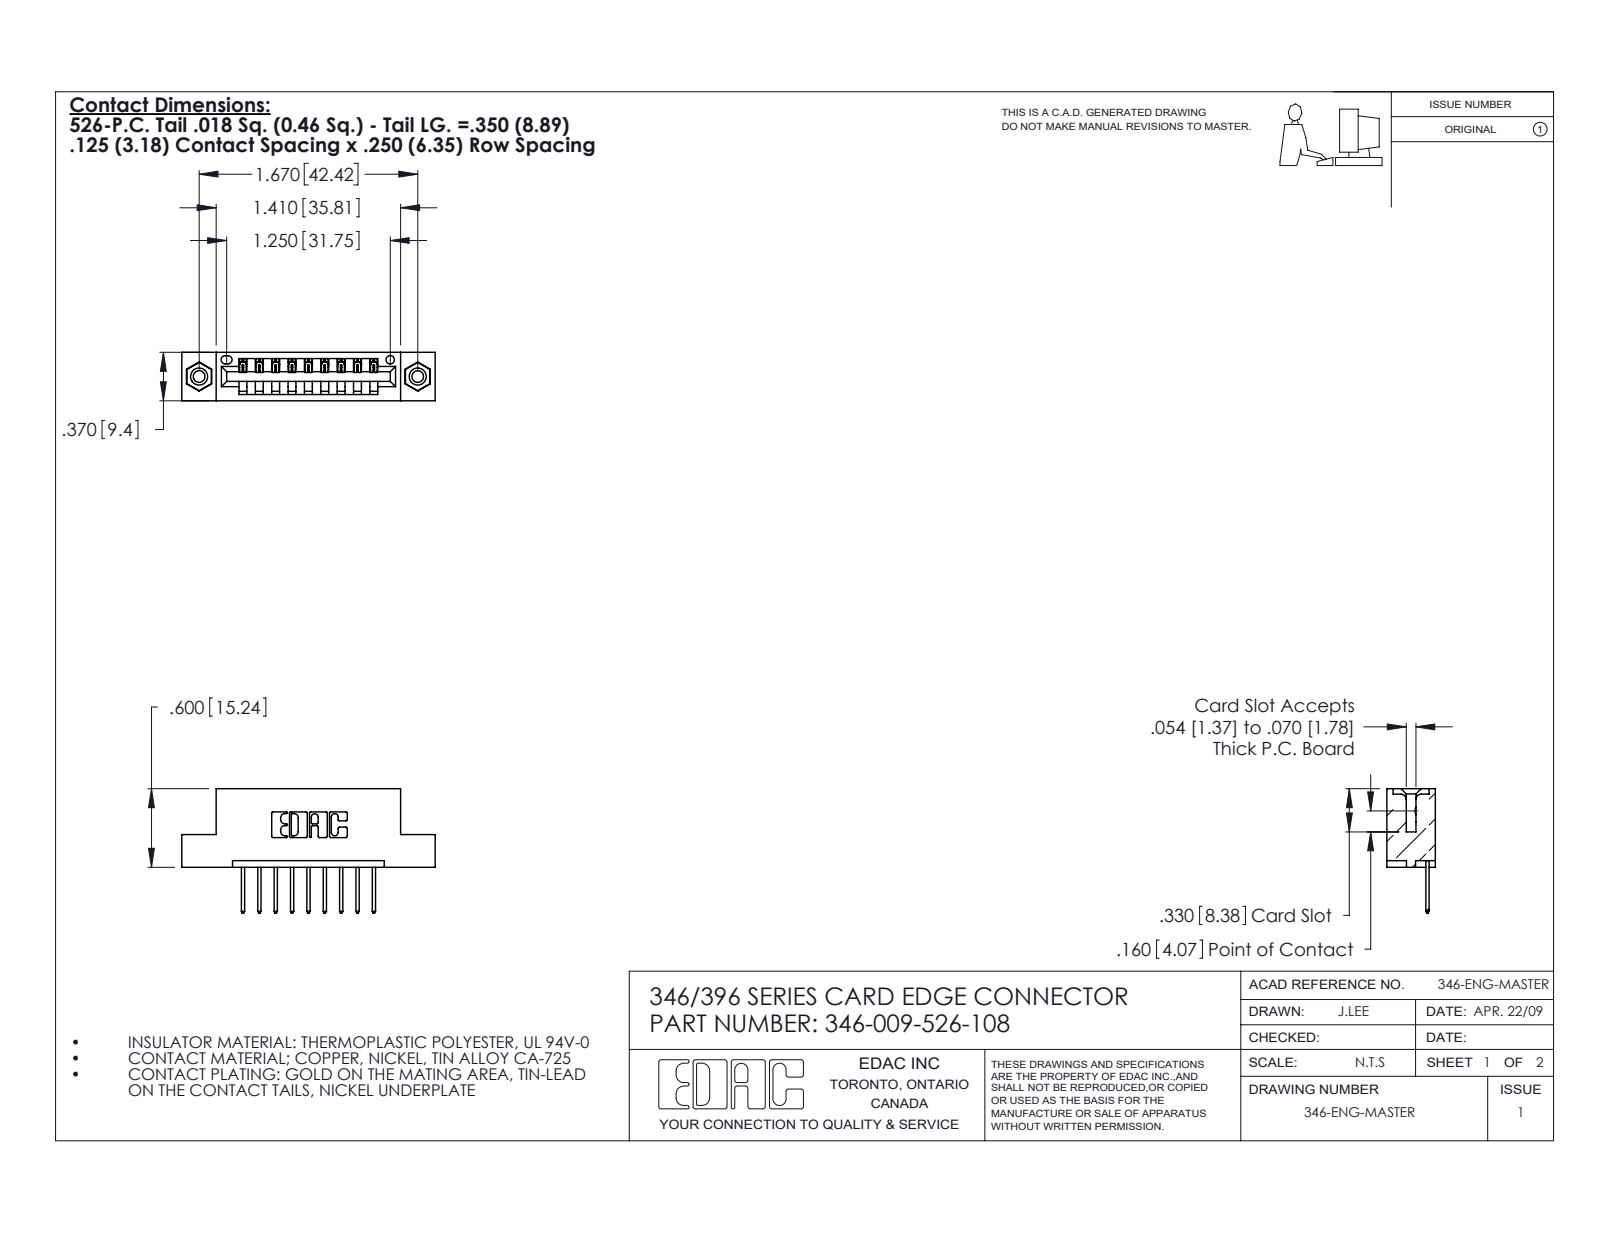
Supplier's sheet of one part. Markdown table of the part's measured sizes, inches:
| quantity | value |
| --- | --- |
| part name | 346-009-526-108; 346 Part_Flush Mounting Lugs - 0.156 Dia-TI; 345-250-001_345-250-003-102; 345-292-001_345-293-126 |
| STEP written by | SolidWorks 2020 (CONFIG_CONTROL_DESIGN) |
| units | inches |
| bodies | 12 solids, 704 faces (468 planar, 220 cylindrical, 16 other) |
| overall size | 1.935 × 0.95 × 0.37 |
| volume | 0.272 in³ |
| surface area | 8.116 in² |
| round holes (diameter × count) | 0.089 × 2, 0.125 × 2, 0.156 × 2, 0.064 × 1 |
| round bosses / shafts (diameter × count) | 0.155 × 2 |
| partial cylindrical surfaces (radius × count) | 0.01 × 22, 0.006 × 18, 0.01 × 18, 0.007 × 6, 0.031 × 6, 0.026 × 3, 0.031 × 2, 0.04 × 2 |
| main face-to-face distances | 0.25, 0.37, 0.048, 0.322, 0.072, 0.298, 0.025, 0.148, 0.222, 0.1 |
| hole center spacings | 0.246, 1.465, 1.67 |
